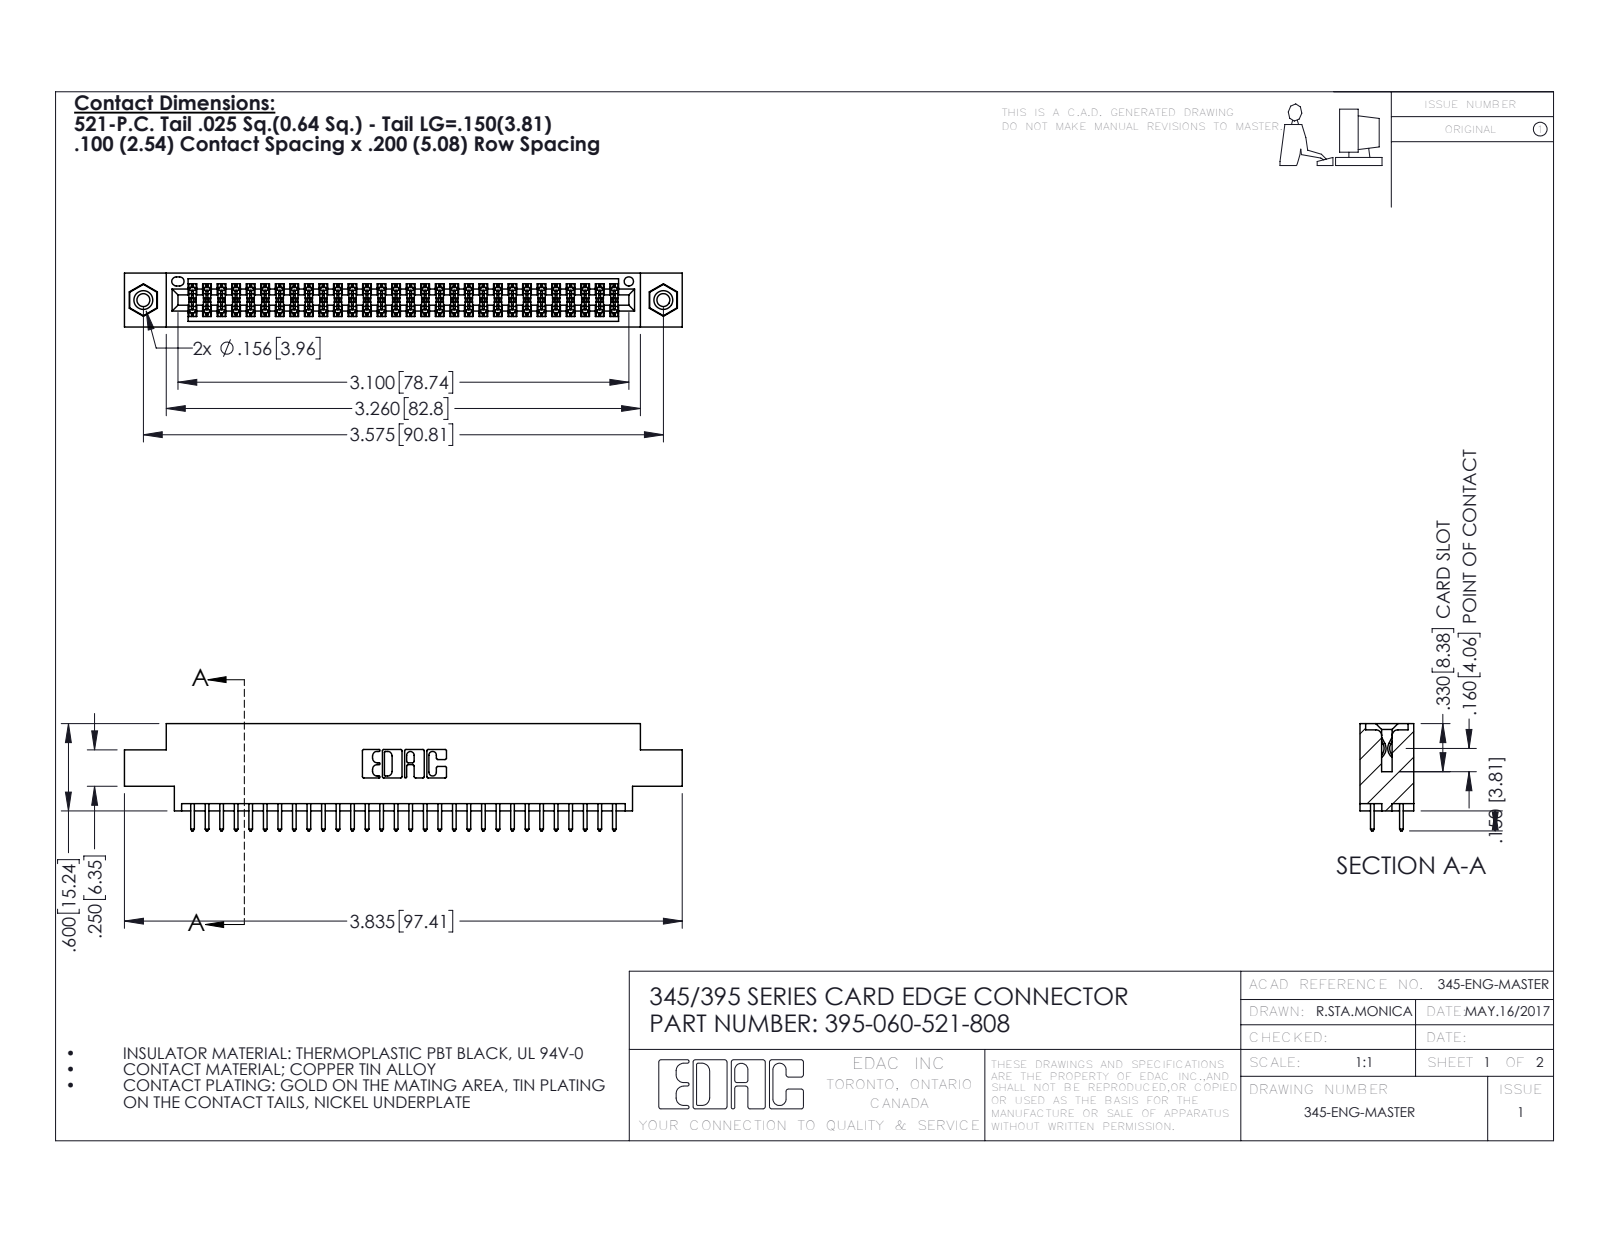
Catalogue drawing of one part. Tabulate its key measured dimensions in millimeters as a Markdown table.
| quantity | value |
| --- | --- |
| part name | 395-060-521-808; 345-250-001_345-250-003-102; 345-292-001_345-293-121; 345 Part_0.170 Offset - 0.156 Dia-TI |
| STEP written by | SolidWorks 2016 (CONFIG_CONTROL_DESIGN) |
| units | millimeters |
| bodies | 63 solids, 3190 faces (2096 planar, 1078 cylindrical, 16 other) |
| overall size | 97.4 × 18.7 × 9.4 |
| volume | 9 210 mm³ |
| surface area | 13 370 mm² |
| round holes (diameter × count) | 2.3 × 2, 3.2 × 2, 4 × 2, 1.6 × 1 |
| round bosses / shafts (diameter × count) | 3.9 × 2 |
| partial cylindrical surfaces (radius × count) | 0.2 × 90, 0.3 × 60, 0.3 × 22, 0.2 × 6, 0.8 × 6, 0.7 × 3, 0.4 × 2, 0.5 × 2 |
| main face-to-face distances | 1.8, 7.6, 9.4, 5.1, 2.5, 6.9, 0.6, 5.7, 4.4, 3.8 |
| hole center spacings | 6.9, 84.8, 90.8 |
